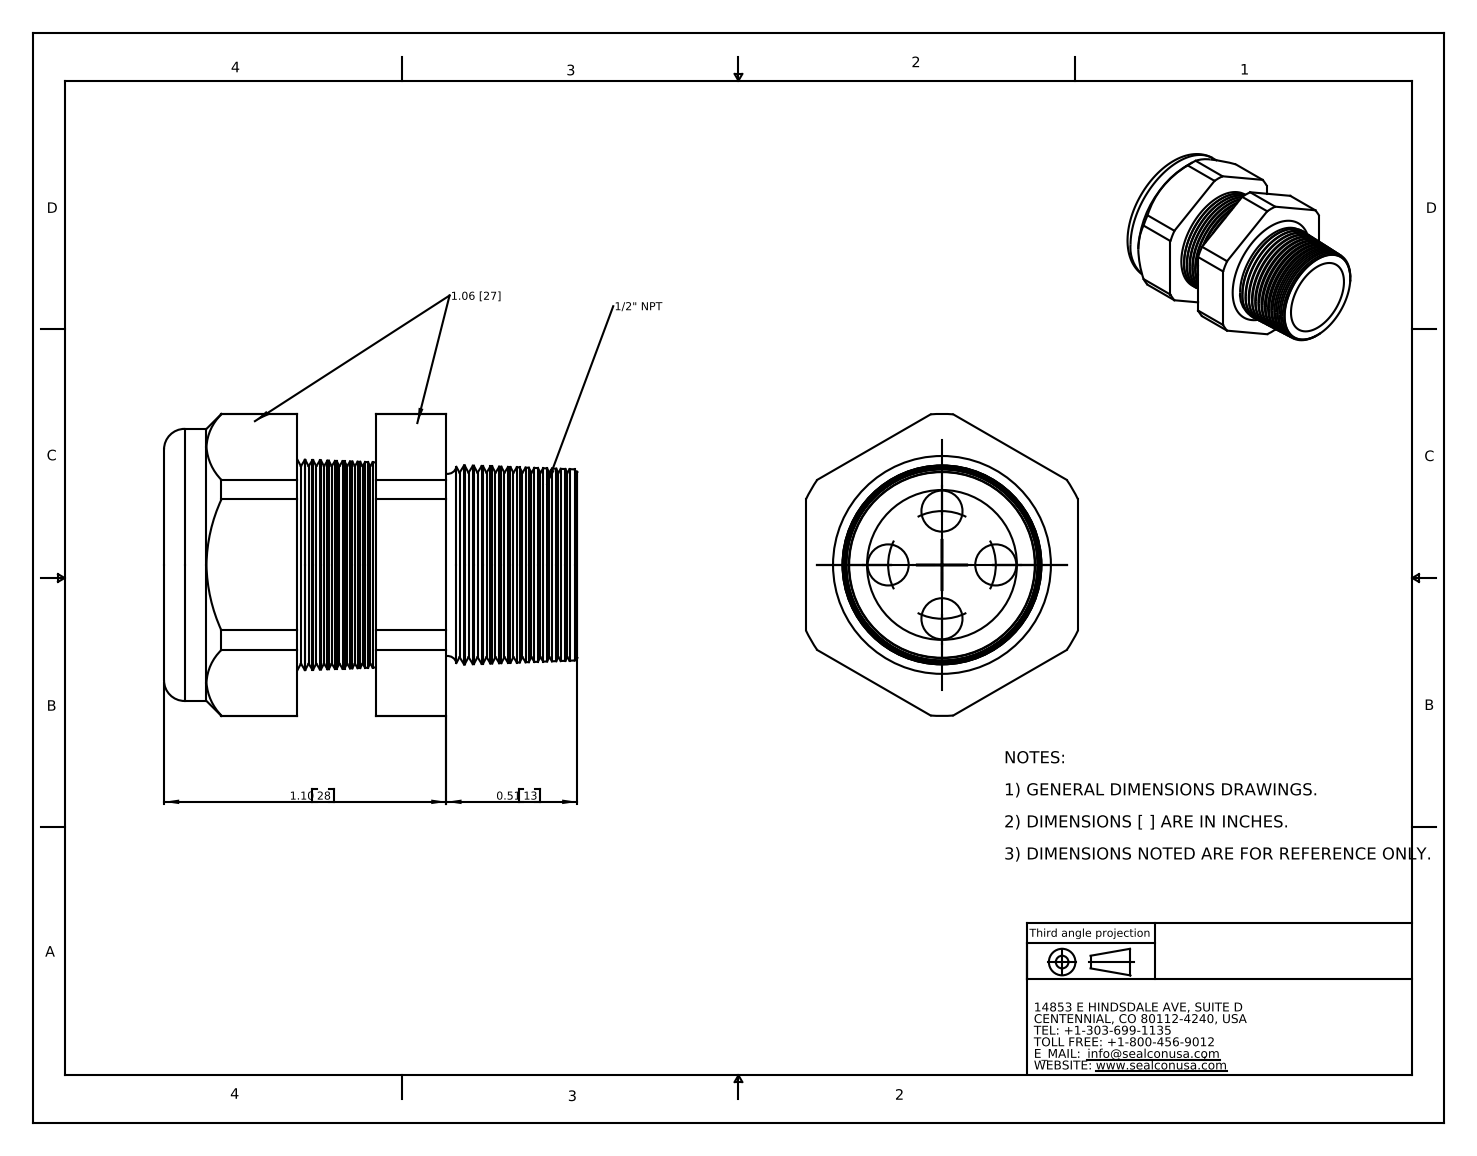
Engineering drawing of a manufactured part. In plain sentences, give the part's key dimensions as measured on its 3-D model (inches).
The part is named "CD16N3-BK". Its 3-D file was written by "SolidWorks 2007 (CONFIG_CONTROL_DESIGN)". It is 2 solids with 206 faces: 20 planar, 28 cylindrical and 158 other. Overall it measures 1.61 by 1.177 by 1.06 inches. Its volume is 0.737 cubic inches and its surface area 13.12 square inches. Round holes: 4 of diameter 0.16, 1 of diameter 0.58, 1 of diameter 0.6. Round bosses or shafts: 1 of diameter 1.06. Partial cylindrical surfaces (rounded edges, fillets, slot ends): 1 of radius 0.588. The main face-to-face distances are 1.06, 0.305, 0.58, 0.276, 0.52, 0.824, 1.1, 0.35, 0.17, 0.474. The hole center spacings are 0.21, 0.297, 0.42.
